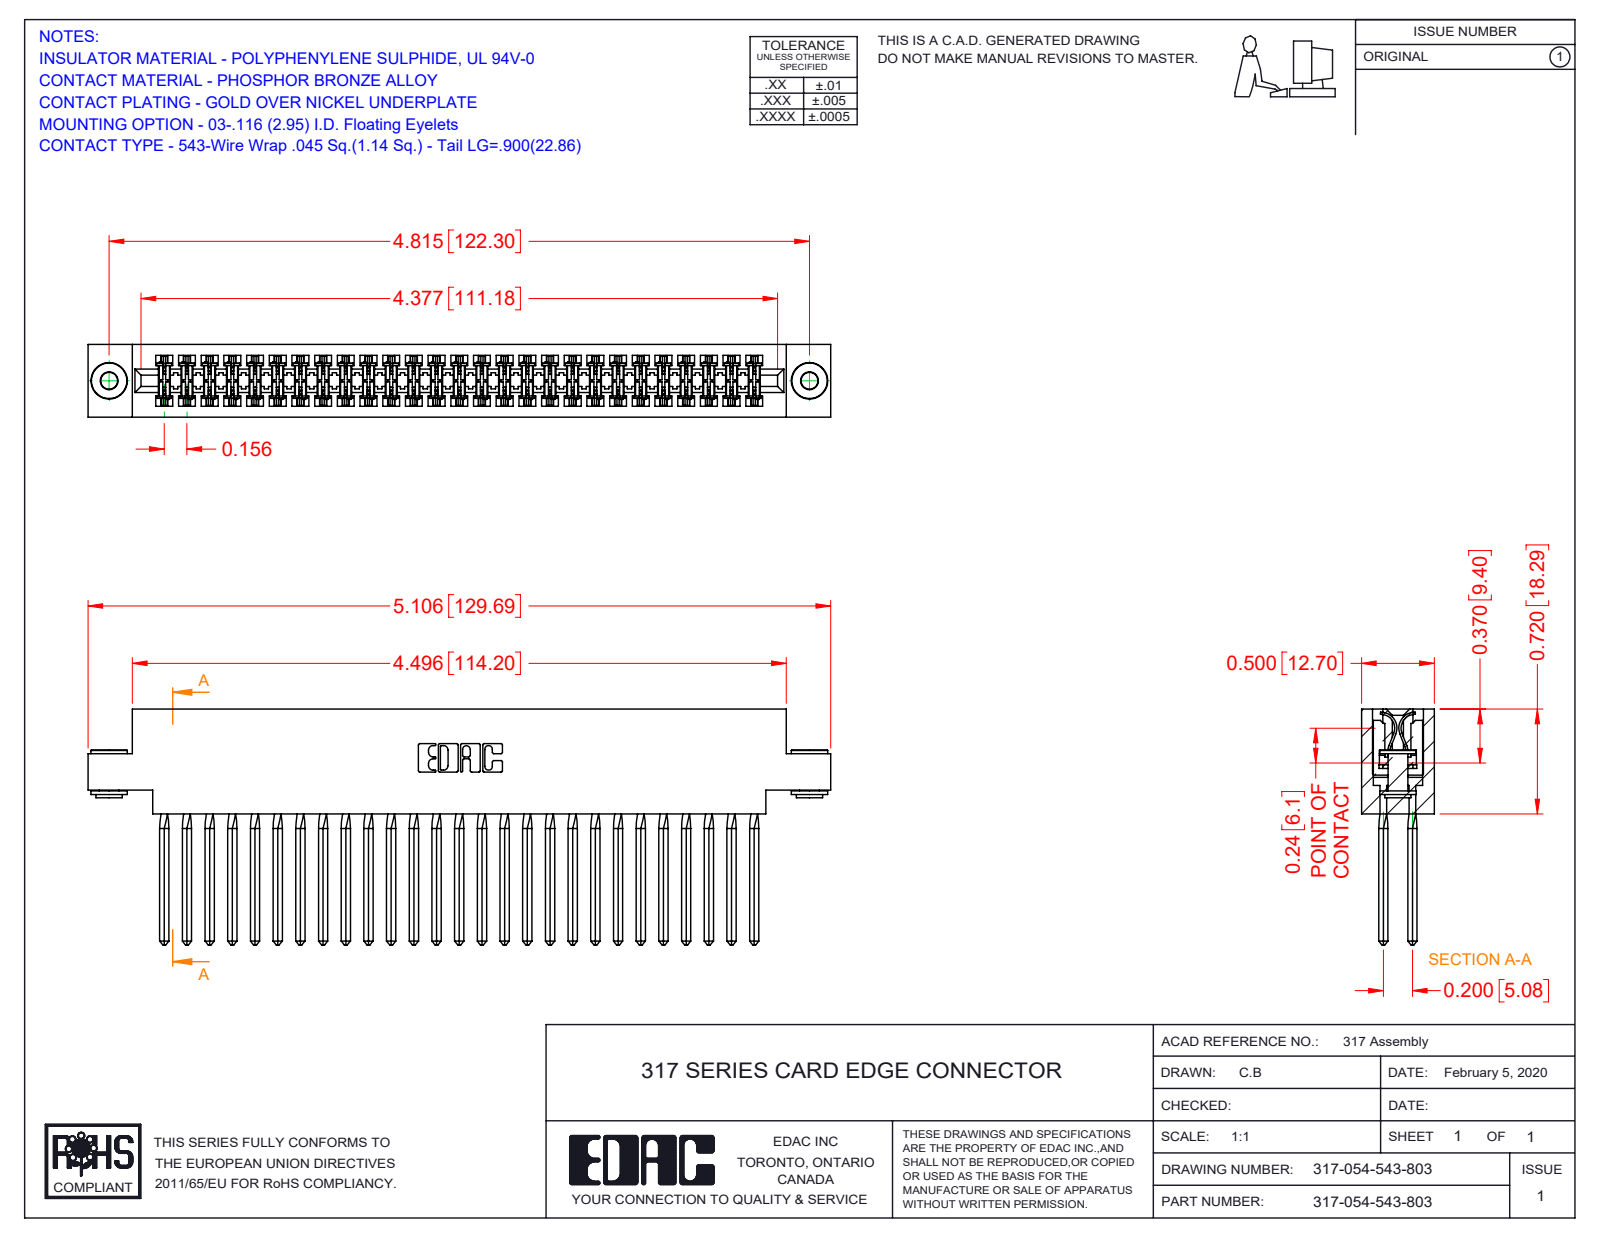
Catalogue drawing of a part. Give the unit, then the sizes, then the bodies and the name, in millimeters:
Units: millimetres
Overall size (bounding box): 129.7 × 41.1 × 12.7
Round holes (diameter × count): ⌀2.9 ×2, ⌀4 ×2
Round bosses / shafts (diameter × count): ⌀6.4 ×2, ⌀4.6 ×2, ⌀3.5 ×2
Partial cylindrical surfaces — rounded edges, fillets, slot ends (radius × count): R0.4 ×108, R0.3 ×22, R0.2 ×6, R0.8 ×6, R0.7 ×3, R2.4 ×2, R2.5 ×2, R2.8 ×2
Main face-to-face distances: 12.7, 1.9, 10.8, 8.9, 2.8, 5, 2.4, 18.3, 5.1, 2.9
Hole centre spacings: 122.3
Volume: 21 550 mm³ · Surface area: 32 310 mm²
Bodies: 57 solids, 4946 faces (4010 planar, 712 cylindrical, 224 other)
Part name (STEP PRODUCT): 317-054-543-803; 345-250-002_345-250-002-102; 317-290-001_543; 317 Part_.156 Dia - TH
STEP written by: SolidWorks 2016 (CONFIG_CONTROL_DESIGN)
